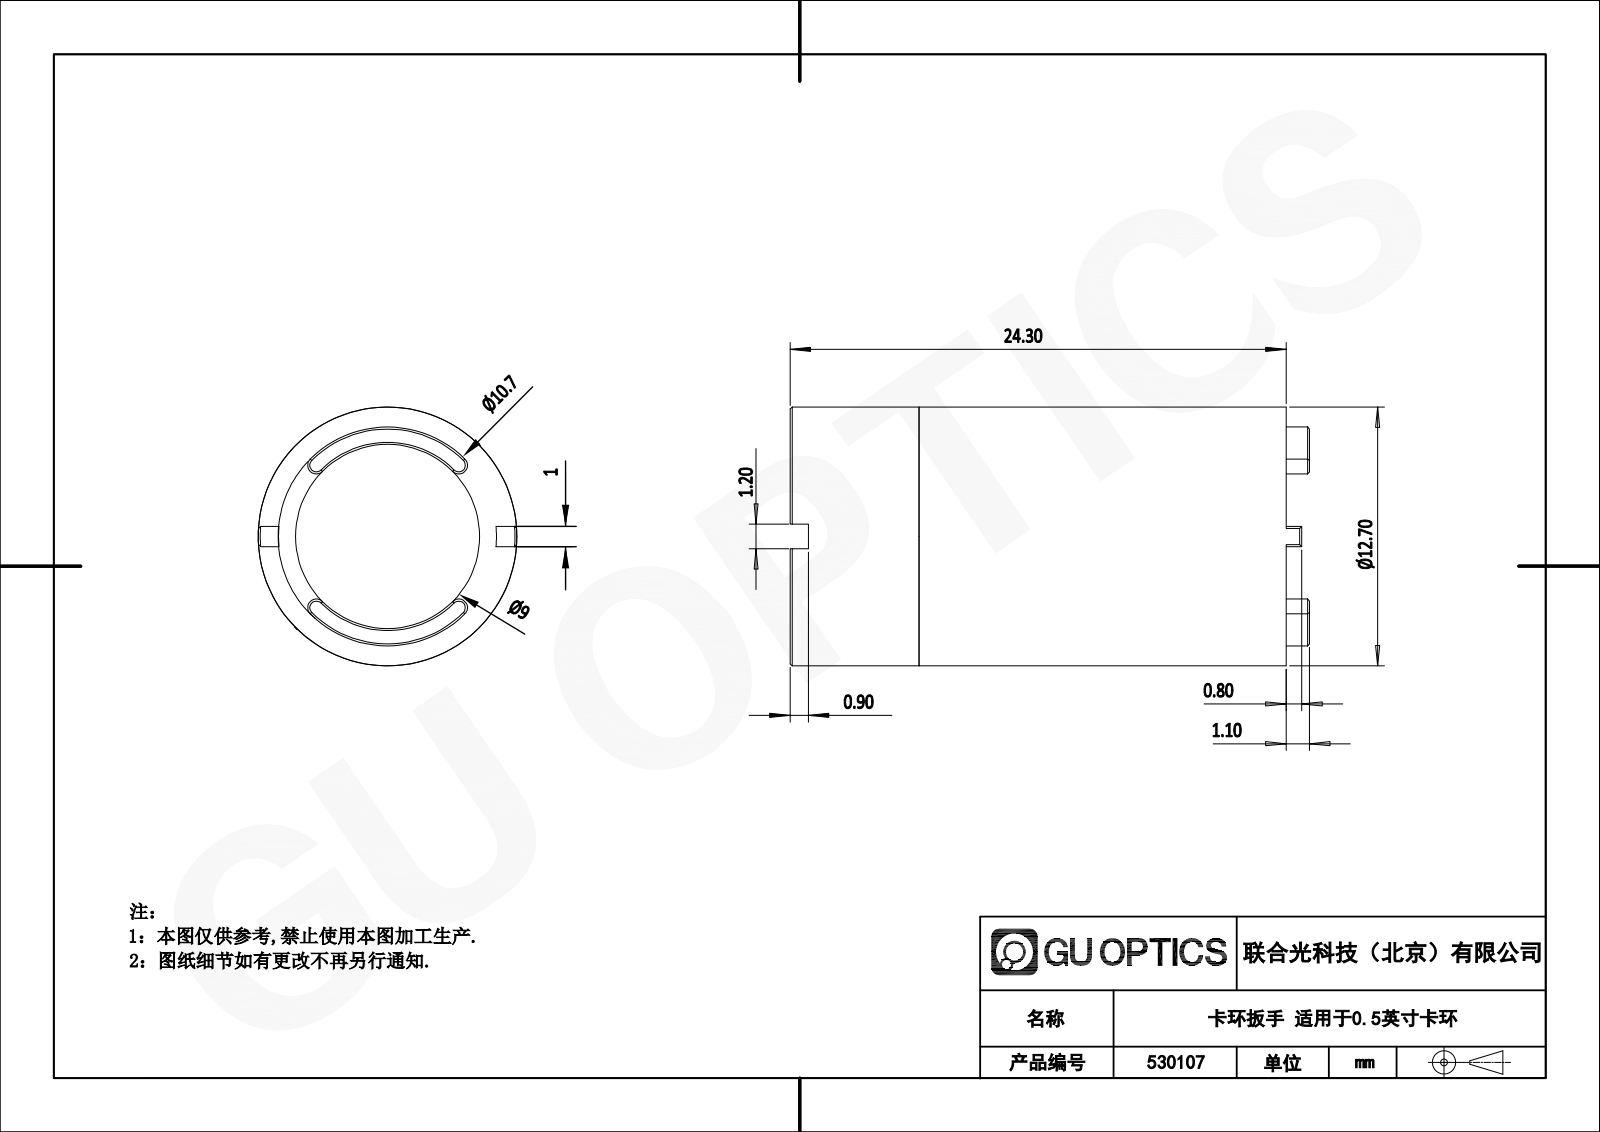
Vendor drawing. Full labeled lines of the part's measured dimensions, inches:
Part name (STEP PRODUCT): 1.8.2.7-ZFG-K05
STEP written by: SolidWorks 2020 (CONFIG_CONTROL_DESIGN)
Units: inches
Bodies: 1 solid, 47 faces (22 planar, 12 cylindrical, 13 other)
Overall size (bounding box): 1 × 0.498 × 0.498
Volume: 0.09 in³ · Surface area: 2.83 in²
Round holes (diameter × count): ⌀0.354 ×1, ⌀0.429 ×1
Round bosses / shafts (diameter × count): ⌀0.498 ×1, ⌀0.498 ×1
Partial cylindrical surfaces — rounded edges, fillets, slot ends (radius × count): R0.017 ×4, R0.21 ×1, R0.211 ×1
Main face-to-face distances: 0.89, 0.065, 0.955, 1, 0.935, 0.045, 0.03, 0.92, 0.043, 0.035
